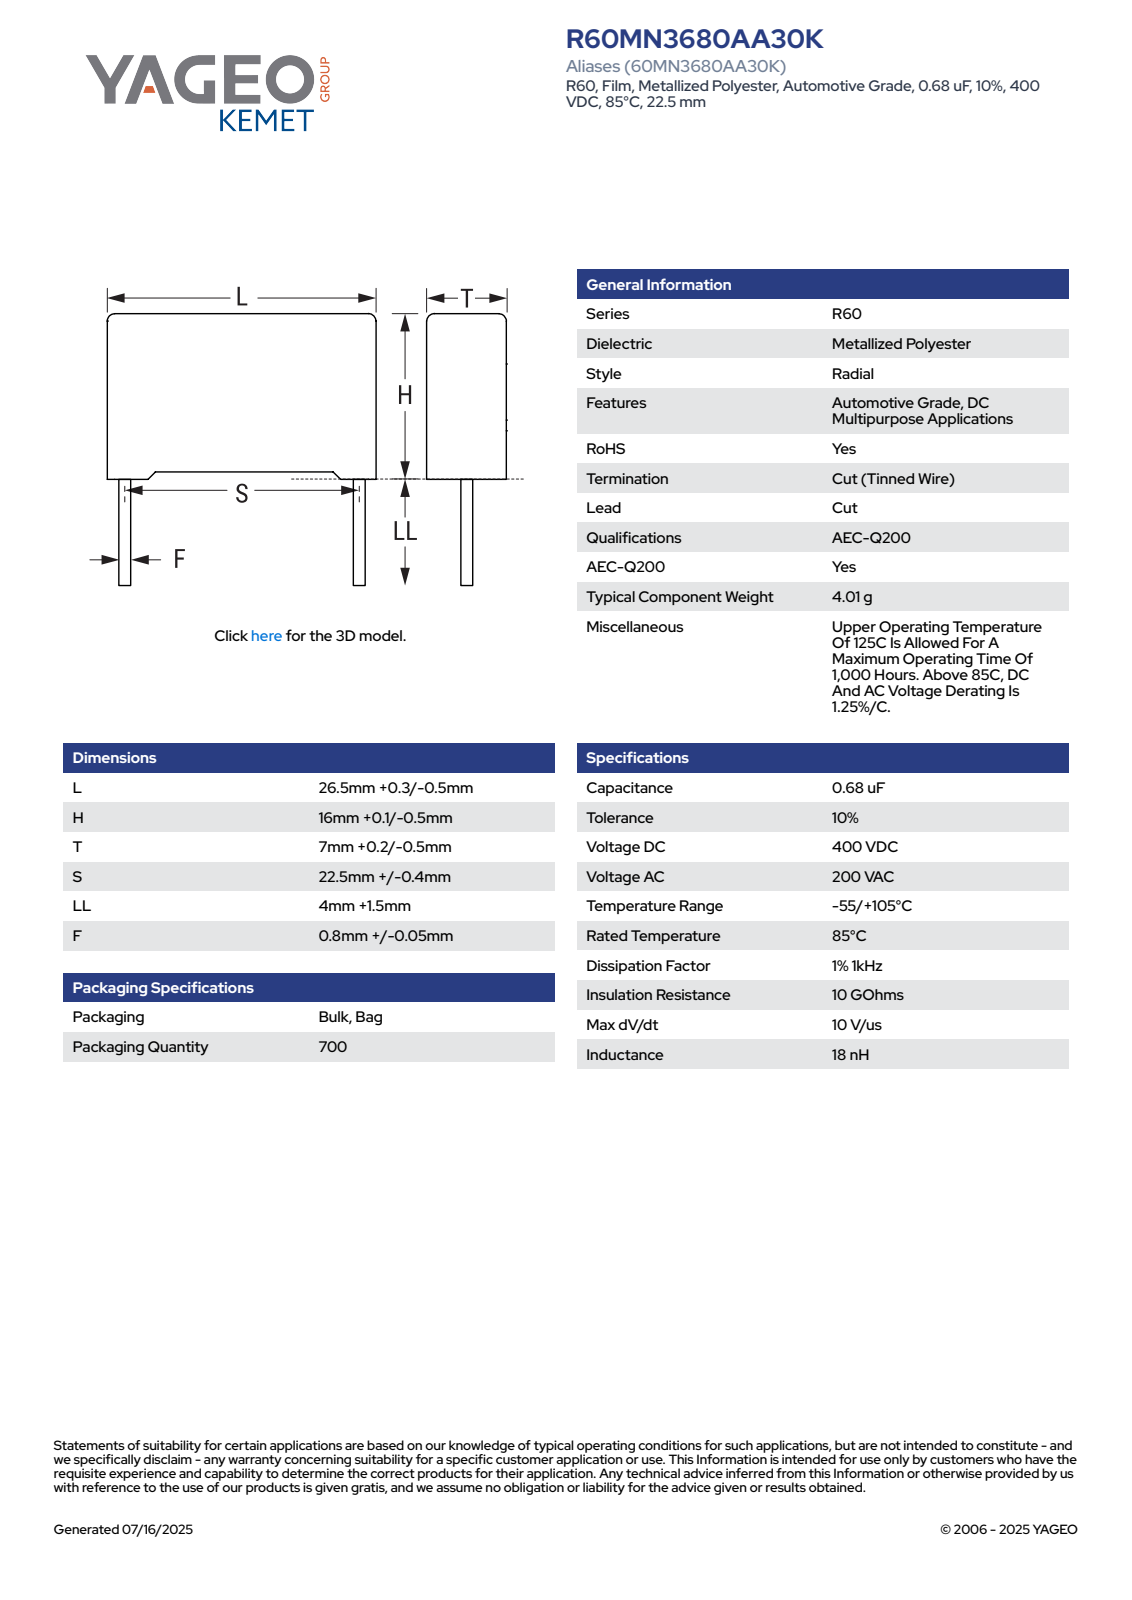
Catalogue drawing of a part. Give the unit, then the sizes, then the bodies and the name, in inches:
Units: inches
Overall size (bounding box): 1.055 × 0.85 × 0.284
Round bosses / shafts (diameter × count): ⌀0.033 ×2
Partial cylindrical surfaces — rounded edges, fillets, slot ends (radius × count): R0.02 ×4
Main face-to-face distances: 0.283, 0.604, 1.055, 0.612, 0.035, 0.022, 0.03, 0.634, 0.248, 0.213
Volume: 0.182 in³ · Surface area: 2.415 in²
Bodies: 4 solids, 85 faces (77 planar, 8 cylindrical, 0 other)
Part name (STEP PRODUCT): CFR_RB2_26.5X16X7_L26.8H16.1T7.2S22.5LL5.5F0.85
STEP written by: SolidWorks 2021 (AUTOMOTIVE_DESIGN)
